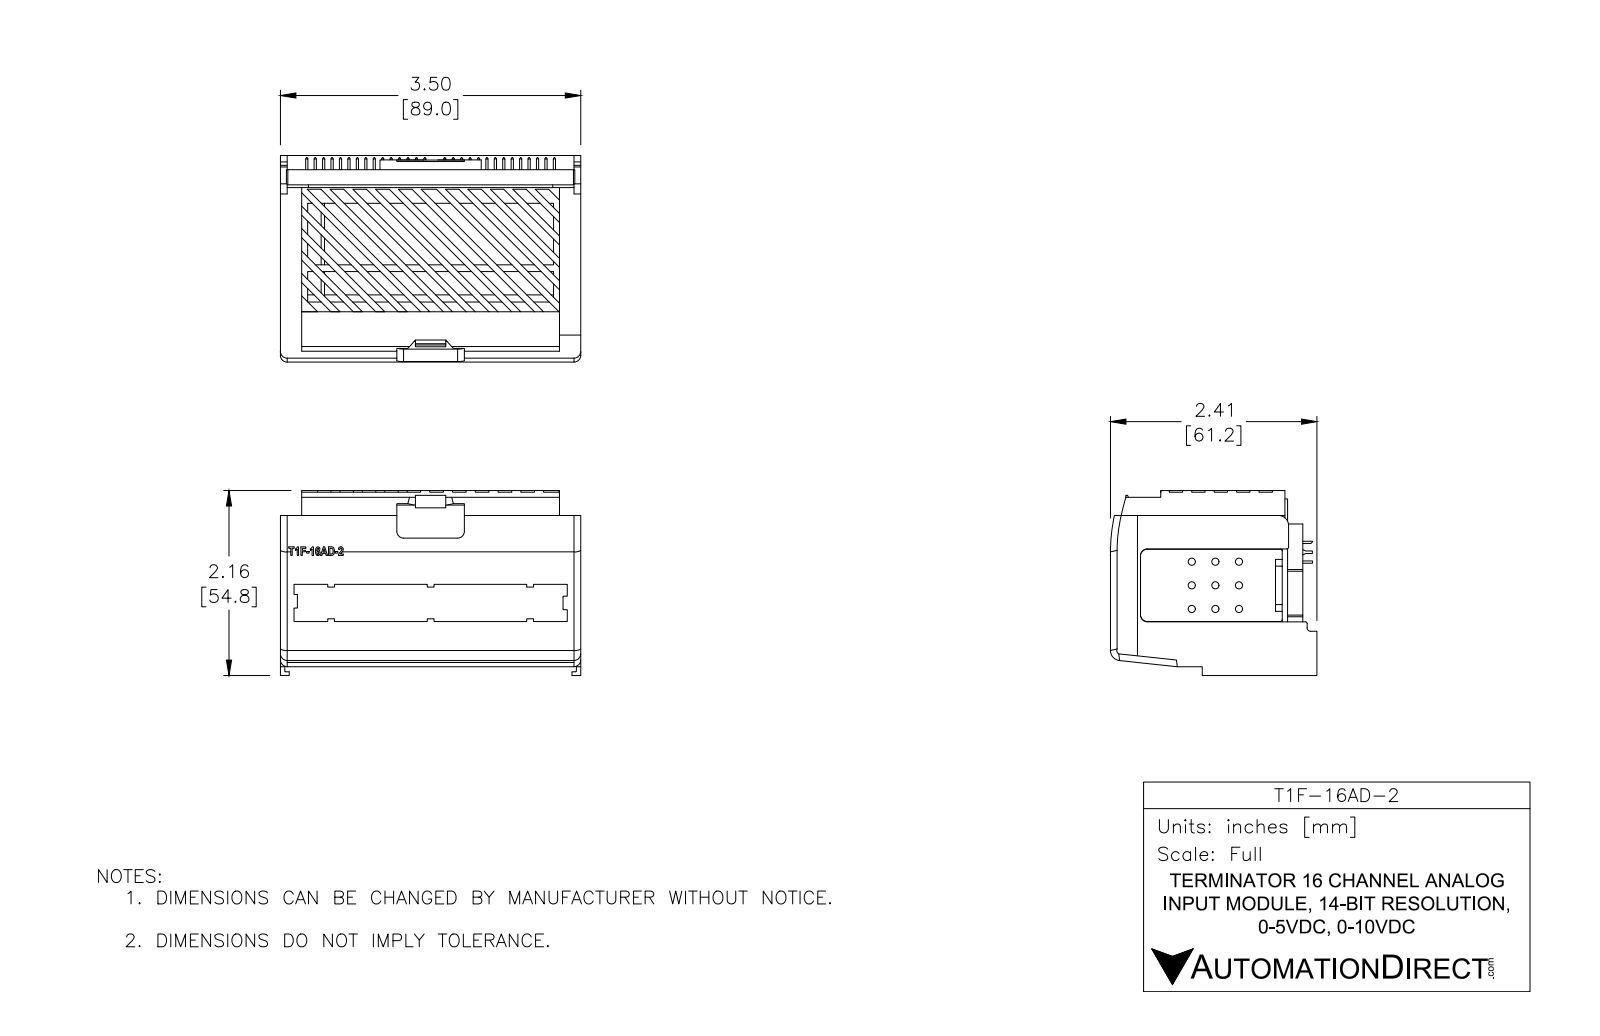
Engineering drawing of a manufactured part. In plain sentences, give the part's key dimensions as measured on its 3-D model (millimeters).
The part is named "T1F-16AD-2". Its 3-D file was written by "SolidWorks 2013 (AUTOMOTIVE_DESIGN)". It is 1 solid with 653 faces: 451 planar, 181 cylindrical and 21 other. Overall it measures 88.7 by 65.1 by 61.36 millimeters. Its volume is 45 450 cubic millimeters and its surface area 54 523 square millimeters. Round holes: 16 of diameter 3. Round bosses or shafts: 56 of diameter 0.7. Partial cylindrical surfaces (rounded edges, fillets, slot ends): 18 of radius 3.5, 5 of radius 1, 3 of radius 0.25, 3 of radius 0.55, 2 of radius 1.5, 1 of radius 8, 1 of radius 10, 1 of radius 18. The main face-to-face distances are 2, 86.7, 55.35, 0.5, 59.8, 88.7, 1.5, 55.26, 53.35, 84.7. The hole center spacings are 5.15, 10.3, 15.45, 20.6, 25.75, 30.9, 36.05, 41.2.
